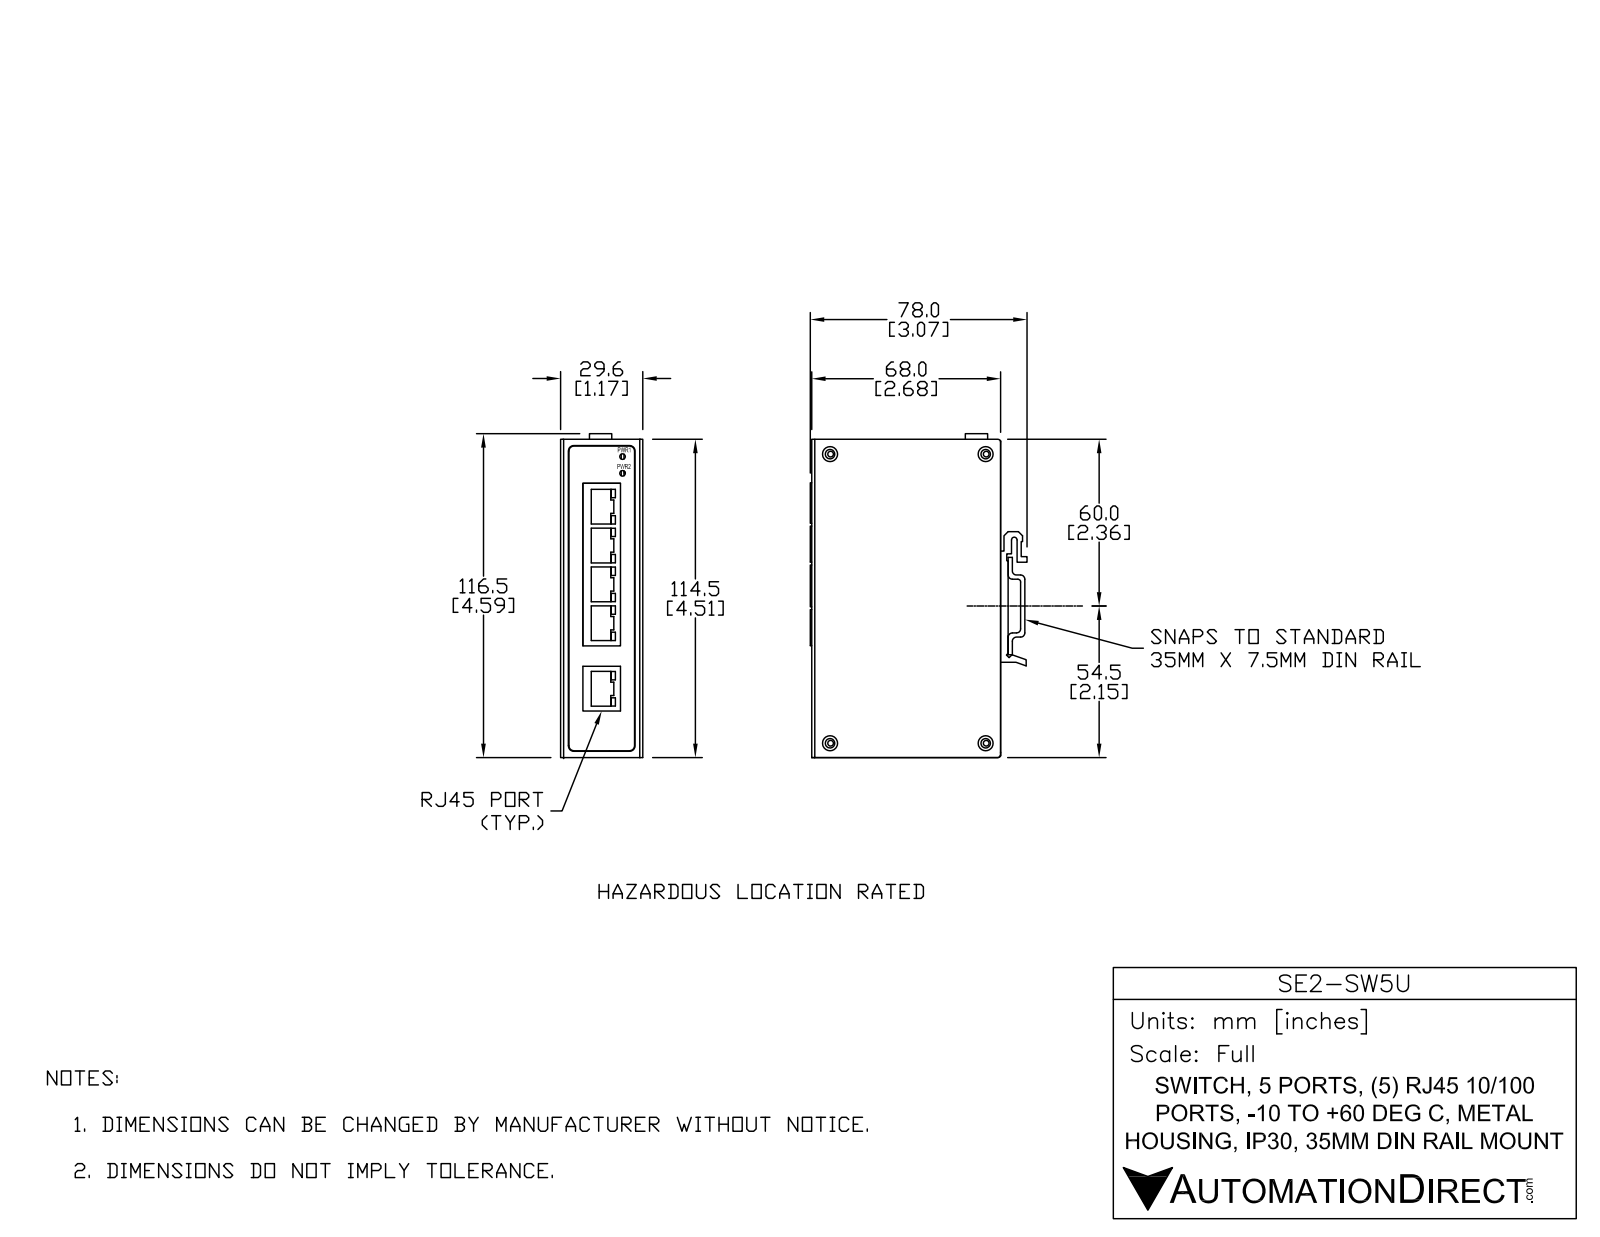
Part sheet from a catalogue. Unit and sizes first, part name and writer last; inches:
Units: inches
Overall size (bounding box): 4.951 × 3.047 × 1.165
Round holes (diameter × count): ⌀0.051 ×4, ⌀0.11 ×4, ⌀0.15 ×4, ⌀0.122 ×3, ⌀0.118 ×2, ⌀0.138 ×2, ⌀0.155 ×1
Round bosses / shafts (diameter × count): ⌀0.142 ×4, ⌀0.118 ×4, ⌀0.051 ×4, ⌀0.024 ×4, ⌀0.197 ×2, ⌀0.315 ×1, ⌀0.157 ×1
Partial cylindrical surfaces — rounded edges, fillets, slot ends (radius × count): R0.024 ×96, R0.026 ×16, R0.079 ×8, R0.118 ×8, R0.041 ×6, R0.039 ×5, R0.012 ×4, R0.112 ×4
Main face-to-face distances: 0.039, 0.02, 1.087, 1.126, 0.079, 1.047, 1.067, 1.106, 0.059, 1.028
Hole centre spacings: 0.2, 2.205, 0.203, 0.4, 0.4, 0.543, 0.543, 0.574
Volume: 3.531 in³ · Surface area: 134.7 in²
Bodies: 10 solids, 938 faces (648 planar, 245 cylindrical, 45 other)
Part name (STEP PRODUCT): SE2-SW5U
STEP written by: SolidWorks 2017 (AUTOMOTIVE_DESIGN)
